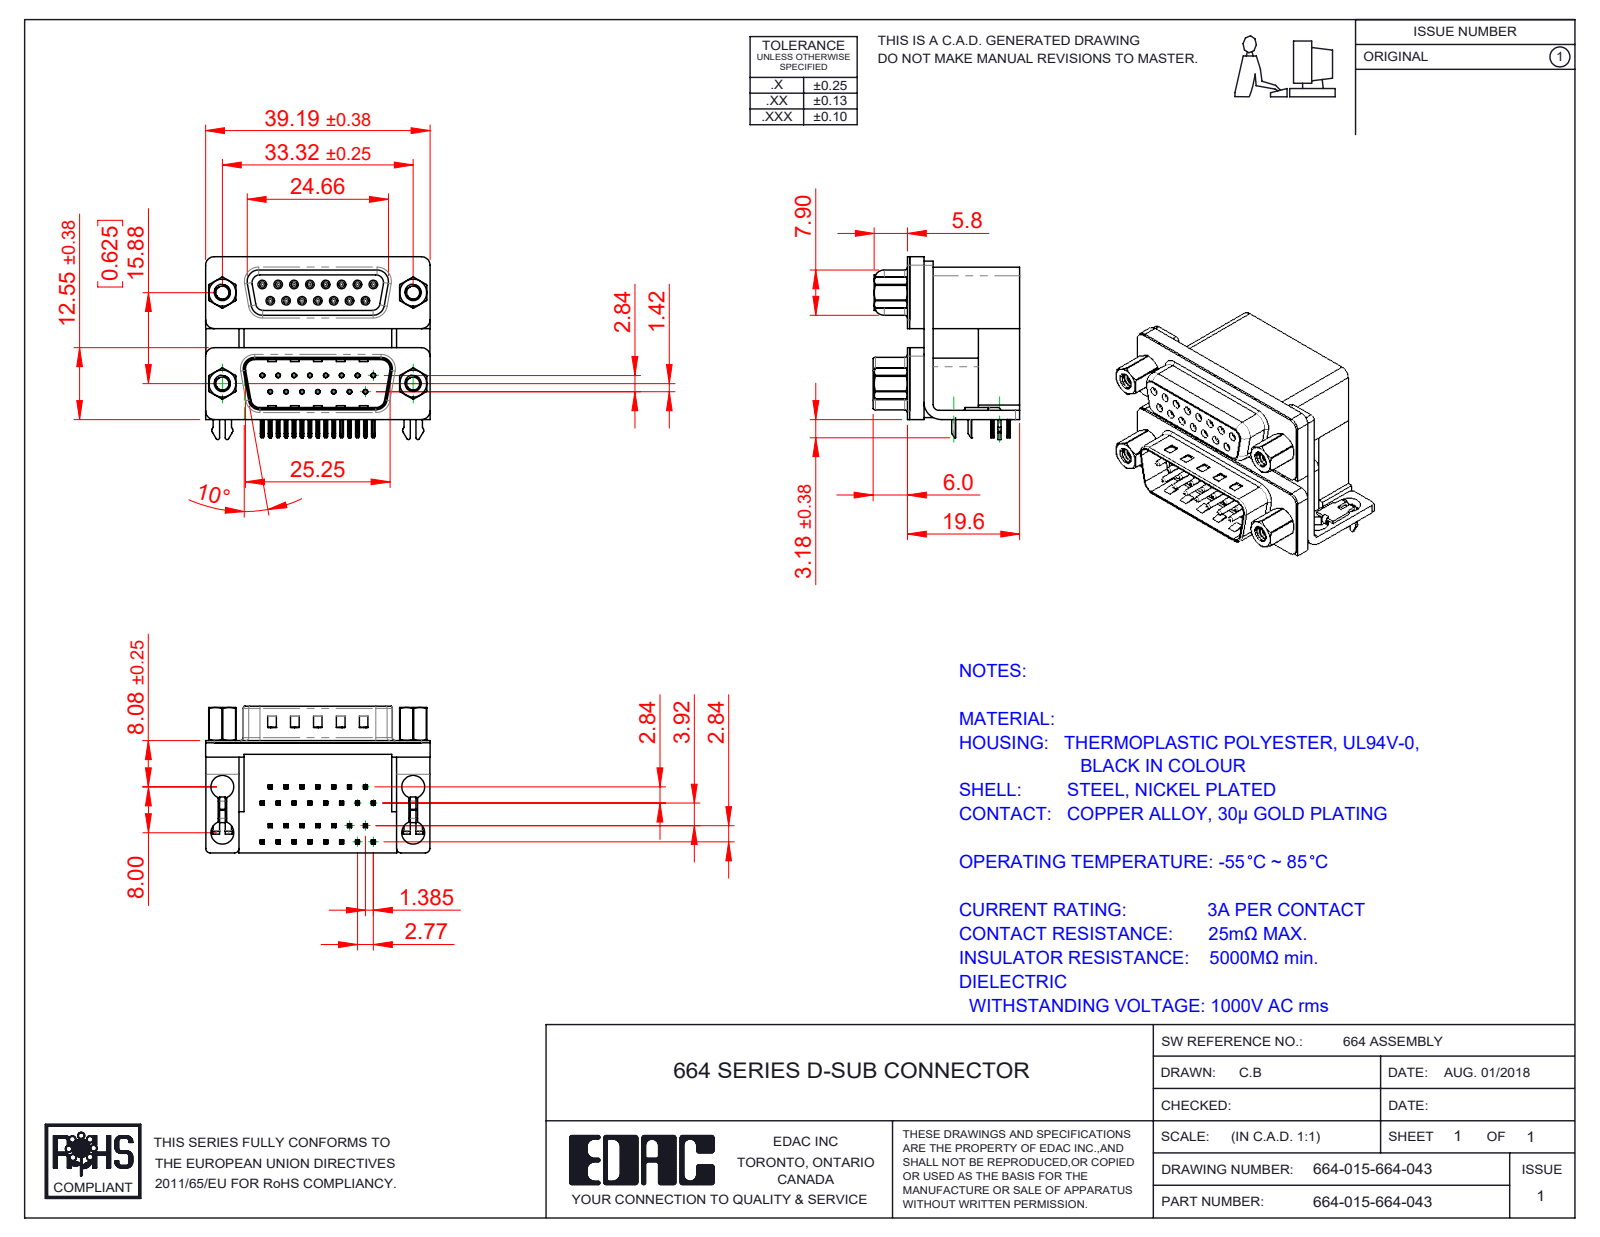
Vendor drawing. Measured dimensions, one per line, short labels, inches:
name: 664 Housing Upper_15 Contacts L; 664 Housing Lower_15 Contacts; 664 Shell Receptacle_15 Contacts; 664 Shell Plug_15 Contacts (+8 more)
written by: SolidWorks 2020 (CONFIG_CONTROL_DESIGN)
unit: in
bodies: 47 solids, 4272 faces (2137 planar, 1188 cylindrical, 947 other)
size: 1.543 × 1.257 × 1.008
volume: 0.912 in³; area: 26.94 in²
holes: 30× ⌀0.031, 15× ⌀0.014, 15× ⌀0.035, 8× ⌀0.157, 4× ⌀0.089, 4× ⌀0.09, 4× ⌀0.138, 4× ⌀0.189, 4× ⌀0.197
bosses: 15× ⌀0.047, 15× ⌀0.03, 4× ⌀0.193, 4× ⌀0.187, 4× ⌀0.154, 4× ⌀0.11
rounds: 121× R0.004, 66× R0.01, 60× R0.006, 30× R0.005, 30× R0.014, 16× R0.02, 16× R0.059, 15× R0.013
face distances: 0.016, 0.756, 0.657, 0.098, 0.283, 0.472, 0.374, 0.086, 0.114, 0.772
hole spacings: 0.124, 0.109, 0.635, 0.218, 0.662, 0.327, 0.625, 0.706
